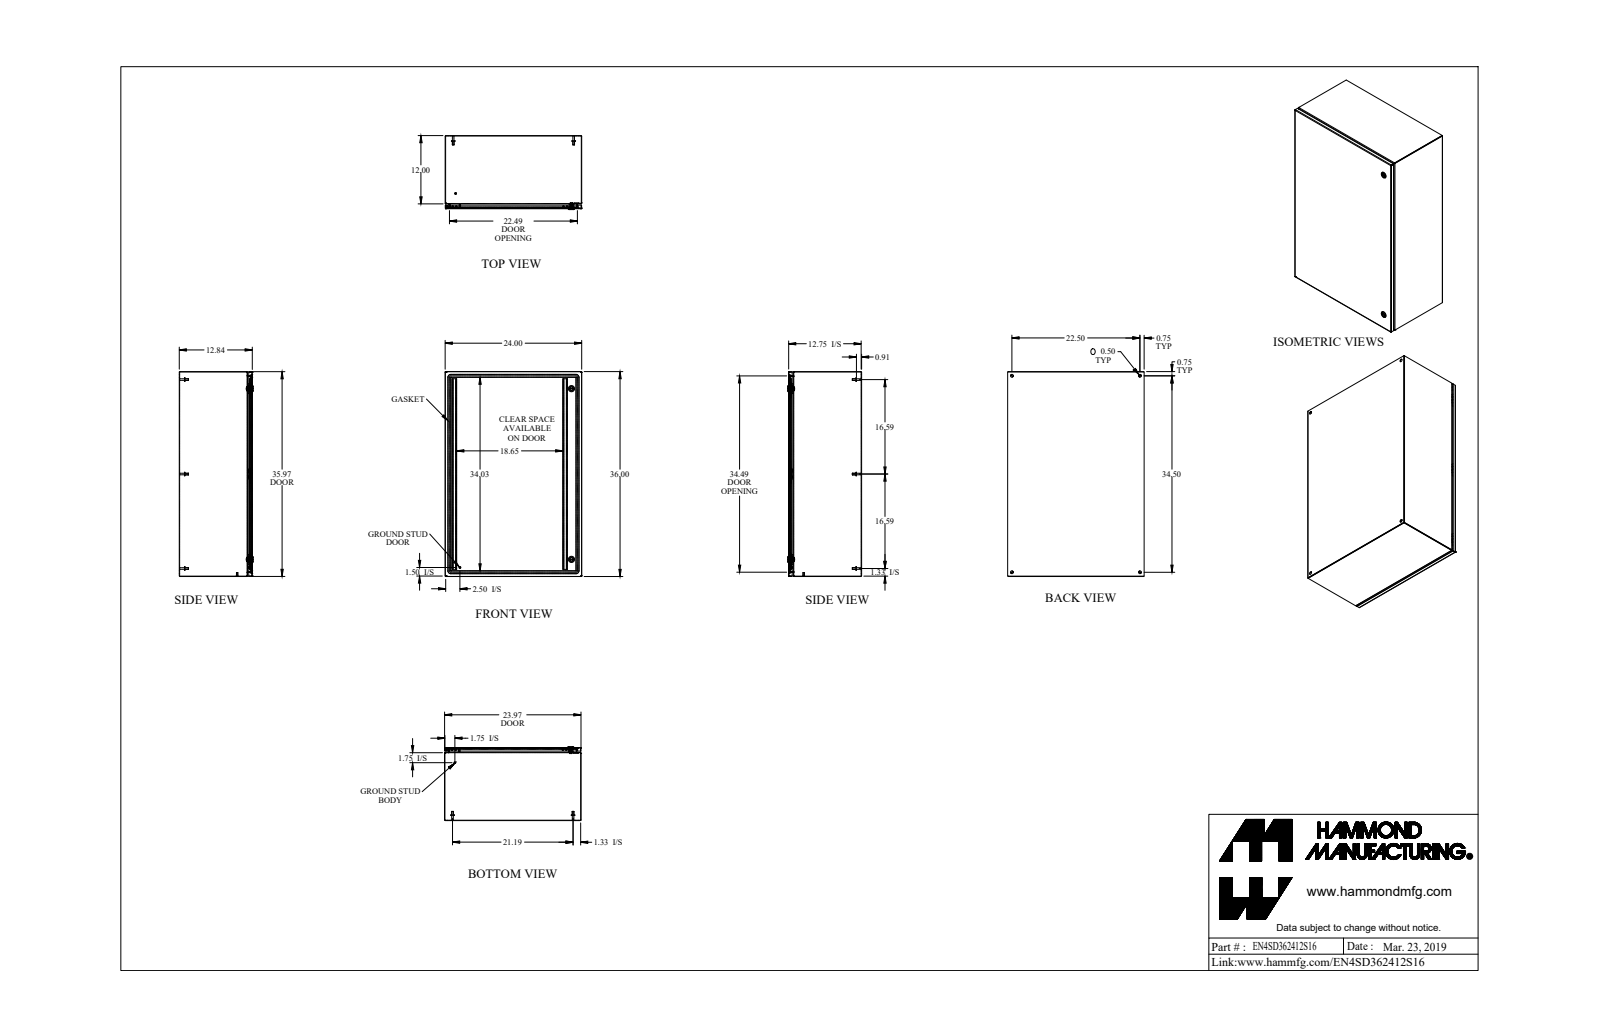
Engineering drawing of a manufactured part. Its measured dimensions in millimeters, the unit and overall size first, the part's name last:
Units: millimetres
Overall size (bounding box): 914.4 × 609.6 × 330.3
Round holes (diameter × count): ⌀12.7 ×6, ⌀5 ×2, ⌀9.8 ×2, ⌀16 ×2, ⌀19.5 ×2, ⌀4.4 ×1, ⌀6.1 ×1, ⌀6.1 ×1
Round bosses / shafts (diameter × count): ⌀15.9 ×8, ⌀8 ×8, ⌀7 ×6, ⌀27.9 ×2, ⌀19.9 ×2, ⌀13.3 ×2, ⌀6.4 ×2, ⌀6 ×2
Partial cylindrical surfaces — rounded edges, fillets, slot ends (radius × count): R0.9 ×18, R2.7 ×18, R0.3 ×12, R1.2 ×12, R7.9 ×12, R0.2 ×6, R1.6 ×6, R3.2 ×4
Main face-to-face distances: 1.8, 324.4, 322.5, 326.2, 607.8, 912.6, 605.9, 609.6, 910.7, 914.4
Hole centre spacings: 547.5, 571.5, 876.3, 1046.2, 63.2, 63.2, 762, 819.6
Volume: 4 280 000 mm³ · Surface area: 4 736 000 mm²
Bodies: 37 solids, 942 faces (454 planar, 308 cylindrical, 180 other)
Part name (STEP PRODUCT): EN4SD362412S16
STEP written by: SolidWorks 2019 (AUTOMOTIVE_DESIGN)
